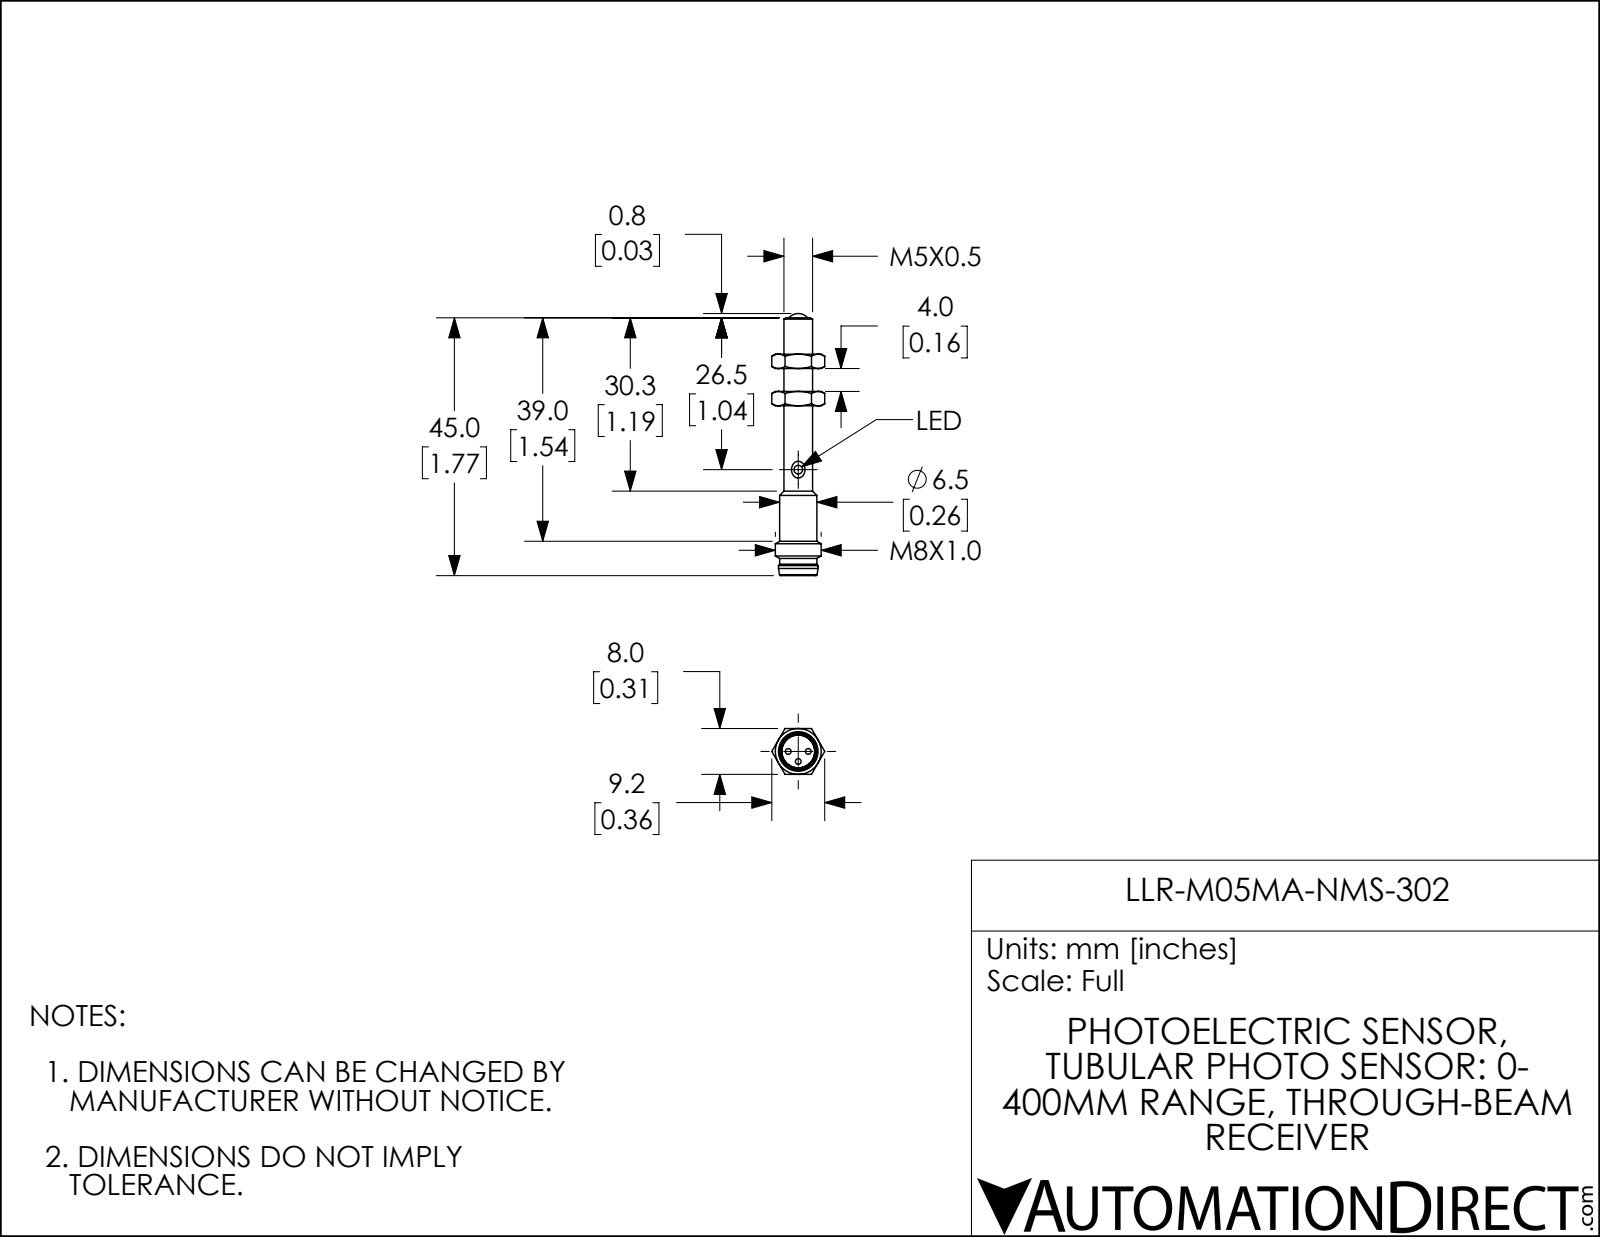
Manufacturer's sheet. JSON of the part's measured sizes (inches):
{"part_name": "LLR-M05MA-NMS-302", "step_written_by": "SolidWorks 2018 (AUTOMOTIVE_DESIGN)", "units": "inches", "bodies": {"solids": 3, "faces": 76, "planar": 20, "cylindrical": 15, "other": 41}, "overall_size": [1.801, 0.364, 0.315], "volume_in3": 0.072, "surface_area_in2": 2.078, "round_holes": [[0.059, 1], [0.197, 1], [0.228, 1]], "round_bosses_or_shafts": [[0.039, 3], [0.315, 1], [0.272, 1], [0.256, 1], [0.224, 1]], "partial_cylinders_radius": [[0.07, 1]], "face_to_face_distances": [0.315, 0.256, 0.098, 0.157, 0.354, 0.974, 1.072, 1.23, 1.328, 1.578]}
